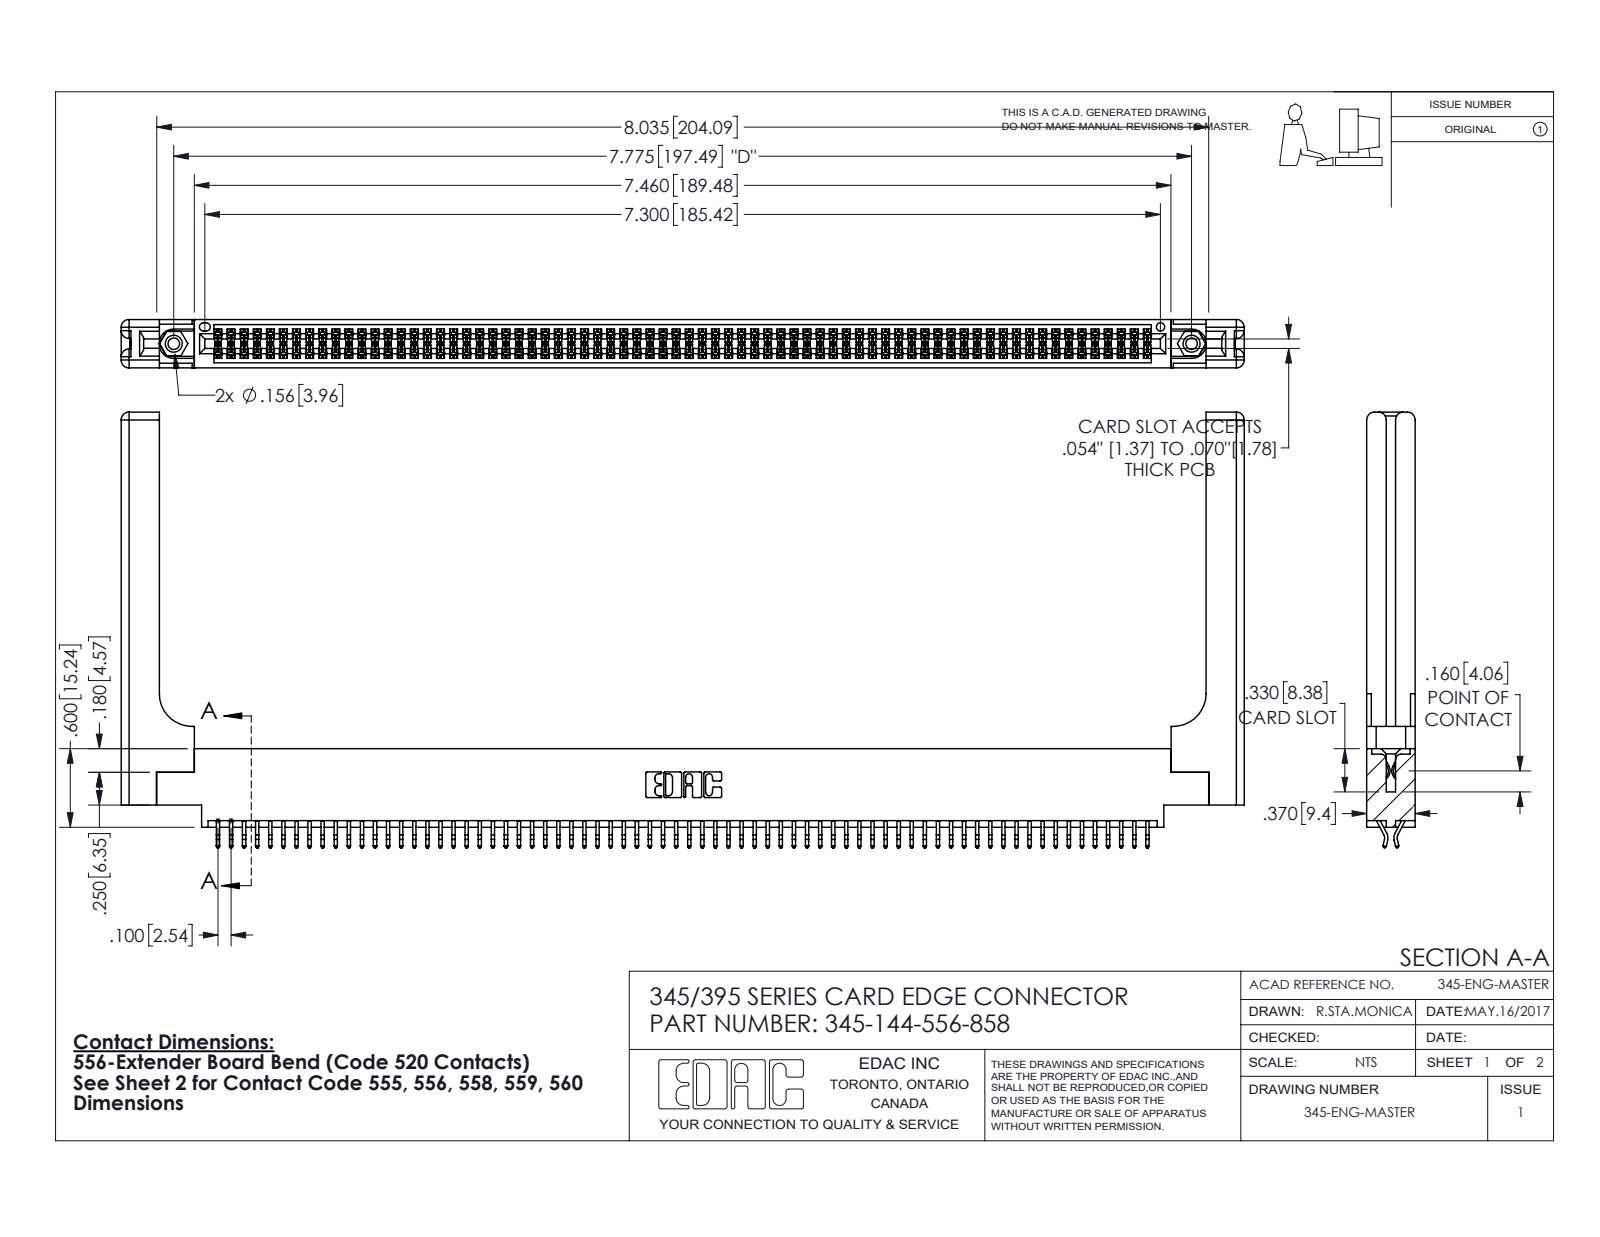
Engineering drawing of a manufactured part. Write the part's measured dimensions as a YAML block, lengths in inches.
part_name: "345-292-001_556 Tail; 345-144-556-858; 345-250-001_345-250-001-102; 345 Part_0.170 Offset - 0.156 Dia-TH (+1 more)"
step_written_by: "SolidWorks 2016 (CONFIG_CONTROL_DESIGN)"
units: inches
bodies: {solids: 149, faces: 8450, planar: 5560, cylindrical: 2830, other: 60}
overall_size: [8.579, 3.327, 0.37]
volume: 1.819
surface_area: 57.63
round_holes:
  - {diameter: 0.089, count: 2}
  - {diameter: 0.125, count: 2}
  - {diameter: 0.156, count: 2}
  - {diameter: 0.064, count: 1}
round_bosses_or_shafts:
  - {diameter: 0.155, count: 2}
partial_cylinders:
  - {radius: 0.006, count: 216}
  - {radius: 0.01, count: 22}
  - {radius: 0.06, count: 16}
  - {radius: 0.007, count: 6}
  - {radius: 0.031, count: 6}
  - {radius: 0.026, count: 3}
  - {radius: 0.01, count: 2}
  - {radius: 0.014, count: 2}
face_to_face_distances: [0.072, 0.298, 0.37, 0.025, 0.098, 0.272, 0.2, 0.225, 0.175, 0.148]
hole_center_spacings: [0.27, 7.539, 7.775]
